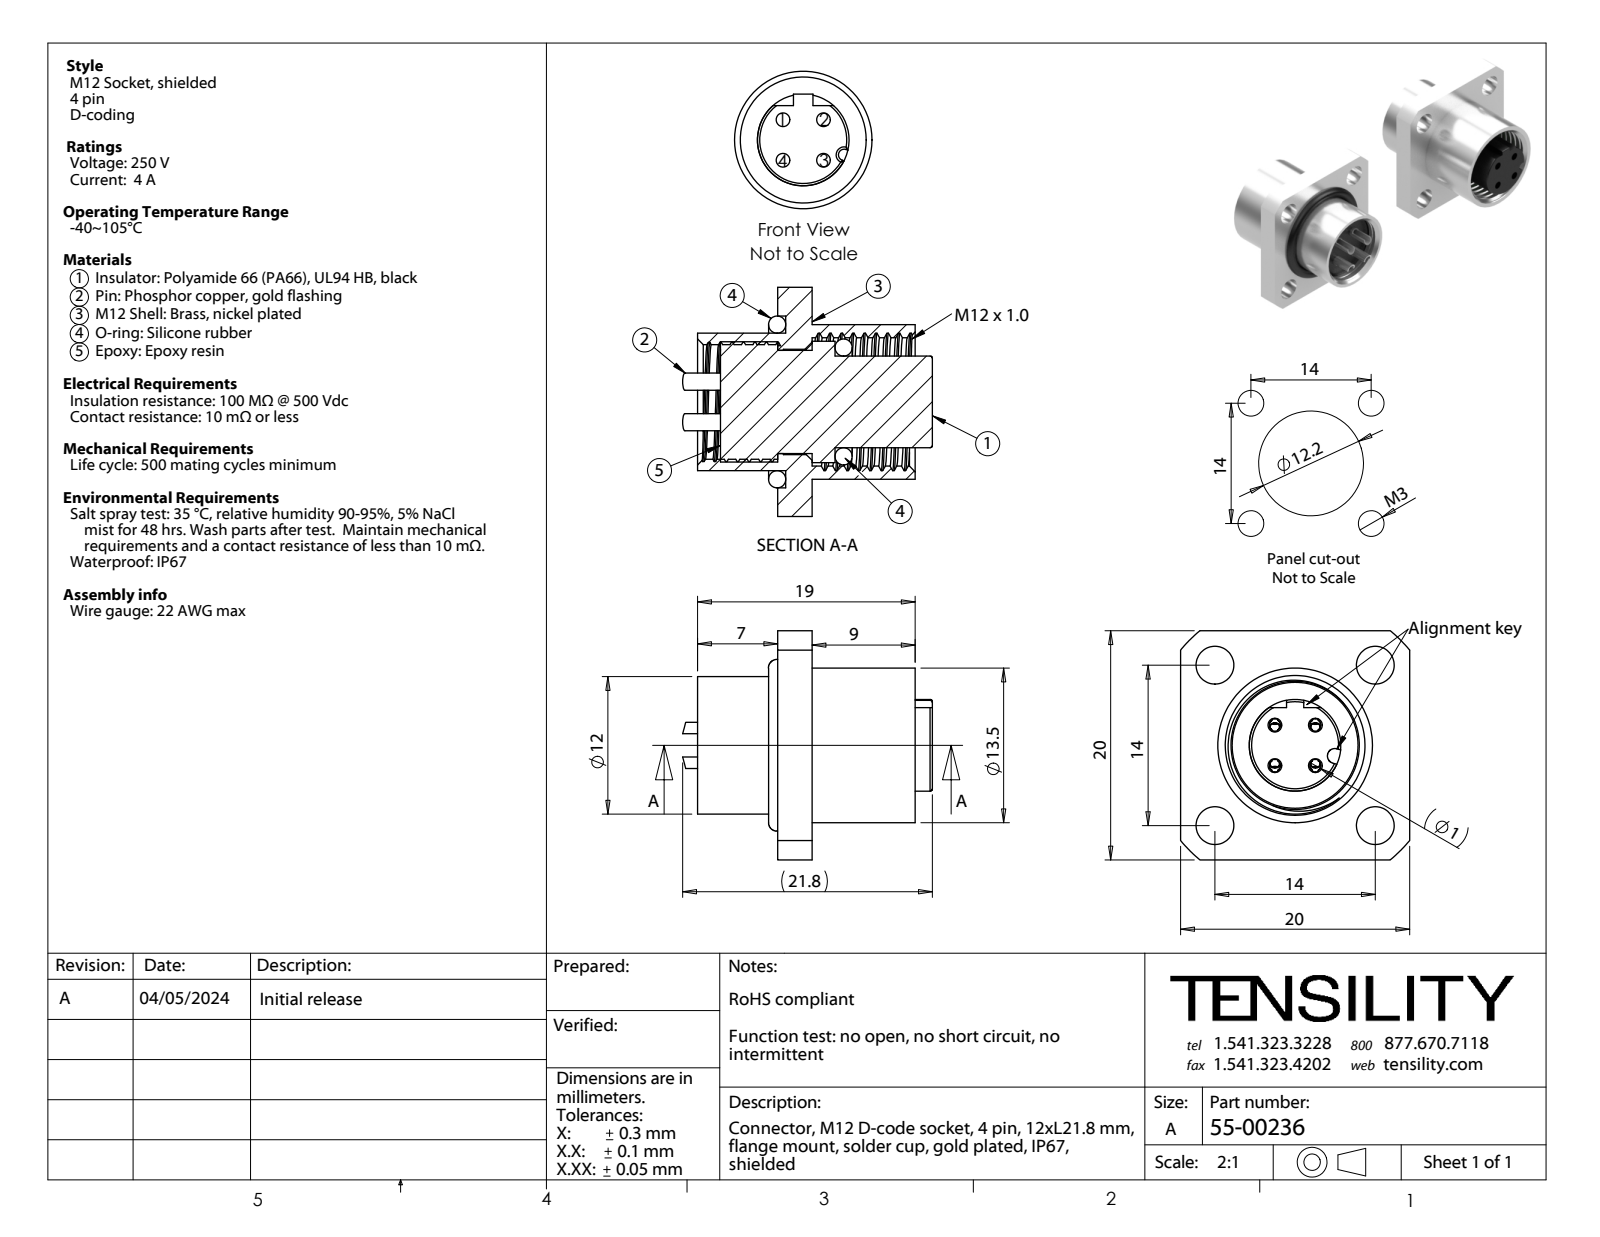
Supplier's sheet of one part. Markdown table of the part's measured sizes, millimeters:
| quantity | value |
| --- | --- |
| part name | 55-00236-04; 55-00236-02; 55-00236-01; 55-00236 (+2 more) |
| STEP written by | SolidWorks 2021 (AUTOMOTIVE_DESIGN) |
| units | millimeters |
| bodies | 8 solids, 478 faces (137 planar, 182 cylindrical, 159 other) |
| overall size | 21.8 × 20 × 20 |
| volume | 2 686 mm³ |
| surface area | 4 543 mm² |
| round holes (diameter × count) | 1.1 × 4, 1.2 × 4, 3.3 × 4, 9 × 1, 9.2 × 1, 10 × 1, 11.2 × 1, 15 × 1 |
| round bosses / shafts (diameter × count) | 1.6 × 4, 1.5 × 4, 13.5 × 1, 12 × 1, 10.6 × 1, 10.5 × 1, 8 × 1 |
| partial cylindrical surfaces (radius × count) | 0.1 × 8, 0.4 × 6, 0.65 × 1, 13 × 1 |
| main face-to-face distances | 3, 5, 20, 8, 5.7, 2.3, 0.7, 2, 10, 7 |
| hole center spacings | 10.21, 2.5, 3.54, 7.4, 9.9, 12.4, 14, 5.01 |
